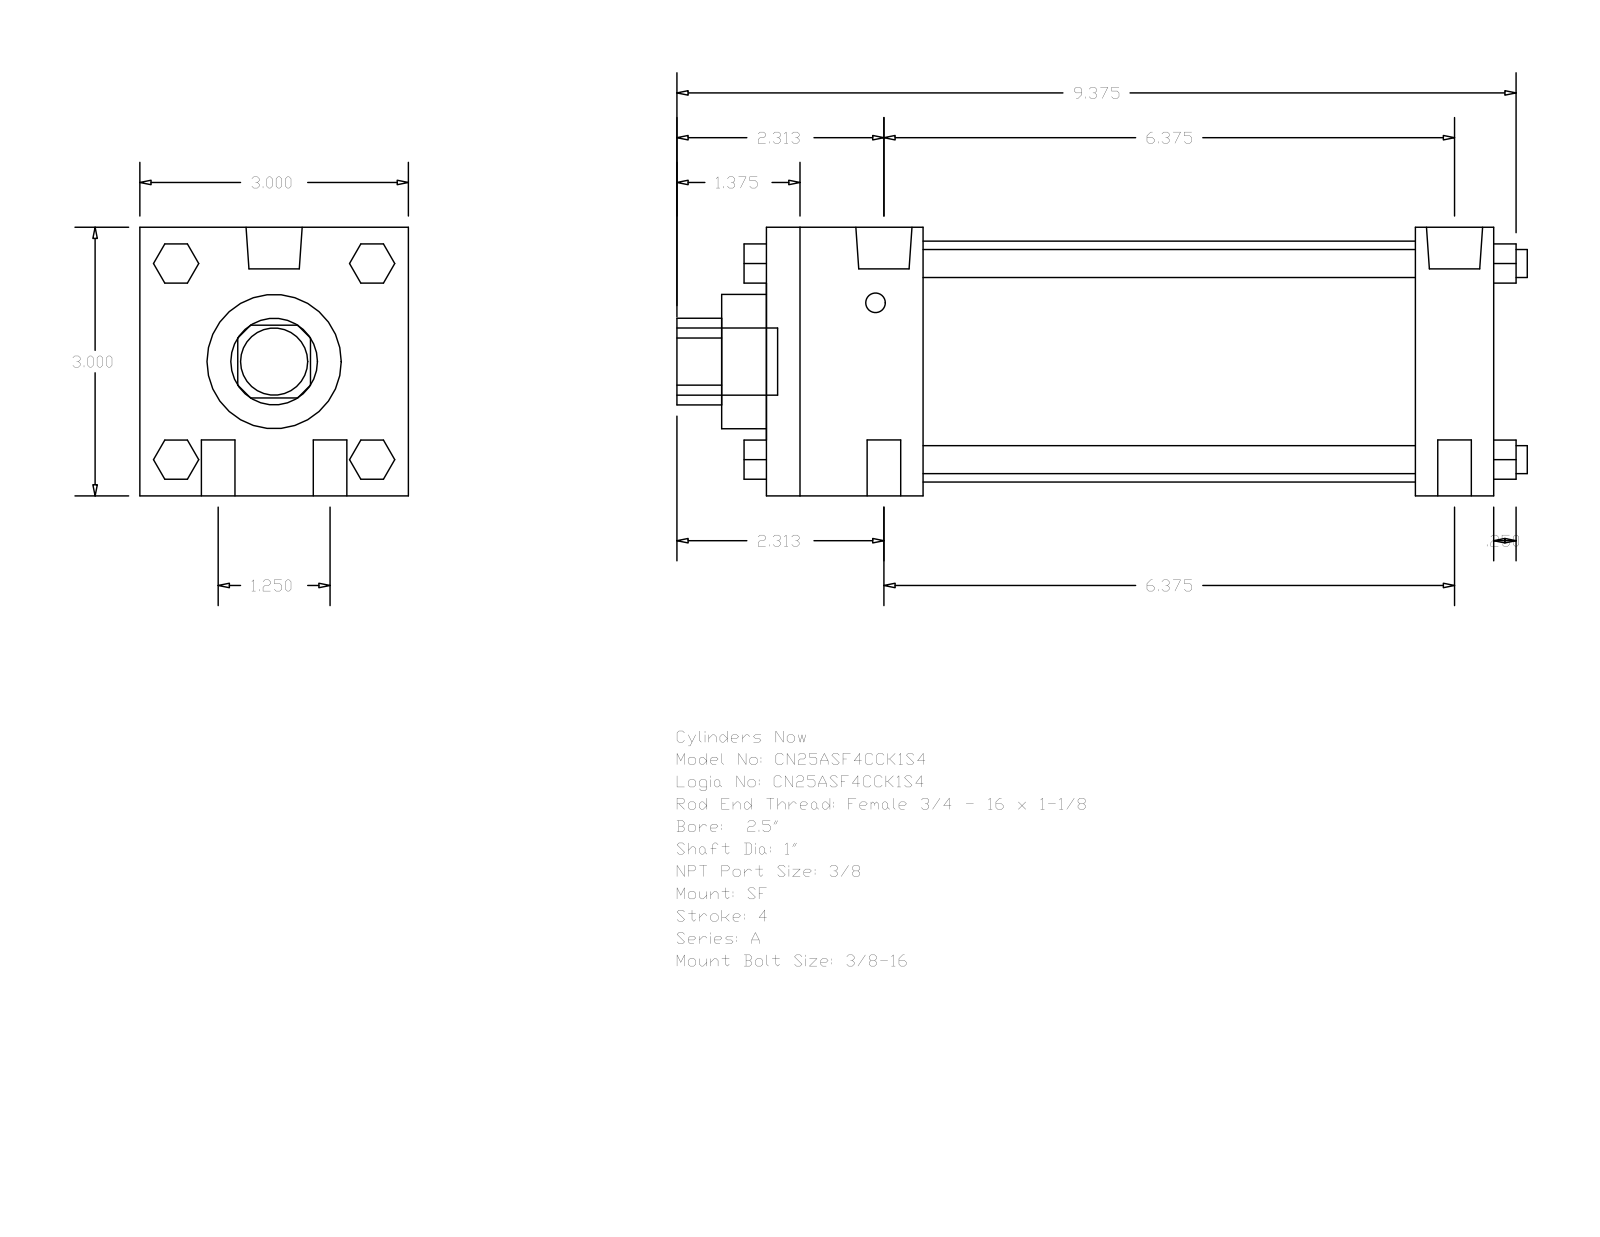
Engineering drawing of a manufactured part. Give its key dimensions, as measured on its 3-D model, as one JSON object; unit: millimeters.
{"part_name": "A_SF__0250_1", "step_written_by": "GSSL Pune (CONFIG_CONTROL_DESIGN)", "units": "millimeters", "bodies": {"solids": 0, "faces": 124, "planar": 94, "cylindrical": 30, "other": 0}, "overall_size": [241.3, 76.2, 76.2], "round_holes": [[25.4, 1], [38.1, 1], [68.33, 1]], "round_bosses_or_shafts": [[9.53, 4], [7.94, 4], [15.93, 2], [5.56, 2], [19.05, 1]], "partial_cylinders_radius": [[12.29, 1]], "face_to_face_distances": [76.2, 206.38, 184.15, 22.23, 44.45, 139.7, 161.93, 12.7, 11.11, 57.15]}
